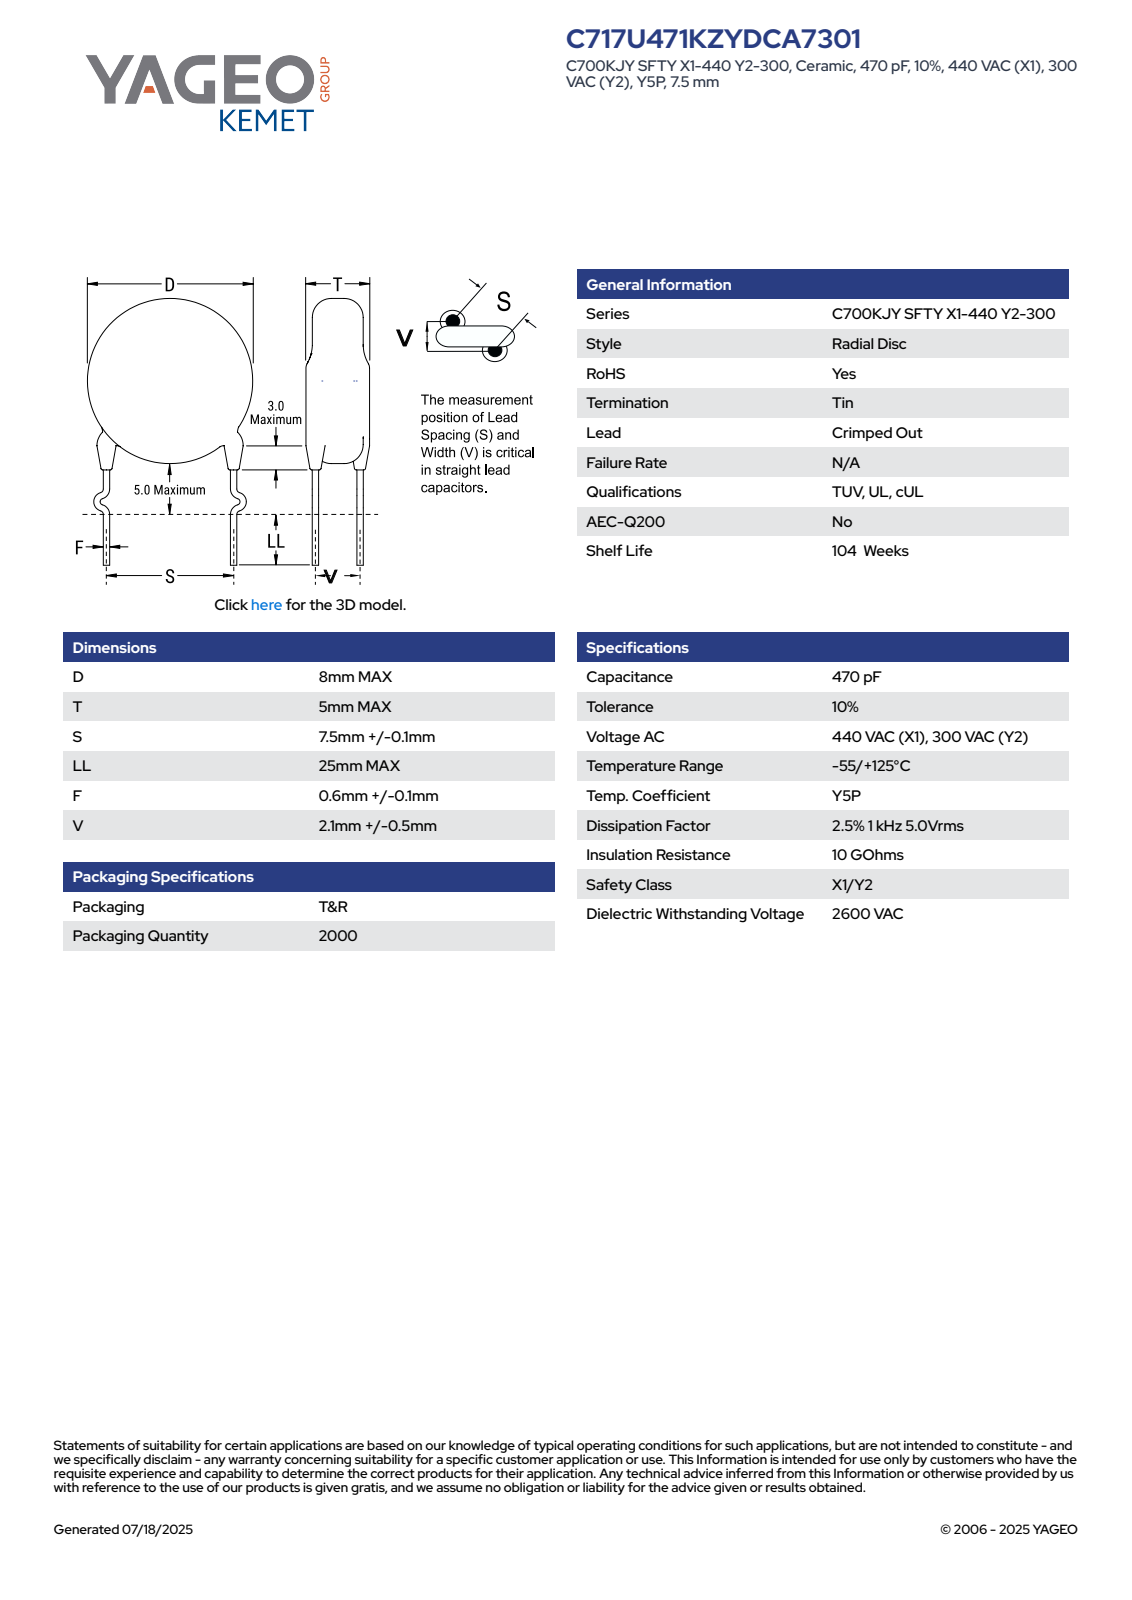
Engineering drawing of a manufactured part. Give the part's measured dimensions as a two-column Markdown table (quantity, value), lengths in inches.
| quantity | value |
| --- | --- |
| part name | CCD_KCO_8X5_D8T5S7.5LL25F0.7V2.1 |
| STEP written by | SolidWorks 2021 (AUTOMOTIVE_DESIGN) |
| units | inches |
| bodies | 4 solids, 113 faces (63 planar, 30 cylindrical, 20 other) |
| overall size | 1.555 × 0.449 × 0.197 |
| volume | 0.017 in³ |
| surface area | 0.58 in² |
| round bosses / shafts (diameter × count) | 0.028 × 8, 0.047 × 4, 0.315 × 1 |
| main face-to-face distances | 0.197, 1.181, 1.417, 0.236, 1.38, 0.199, 0.037, 0.038, 0.03, 0.016 |
